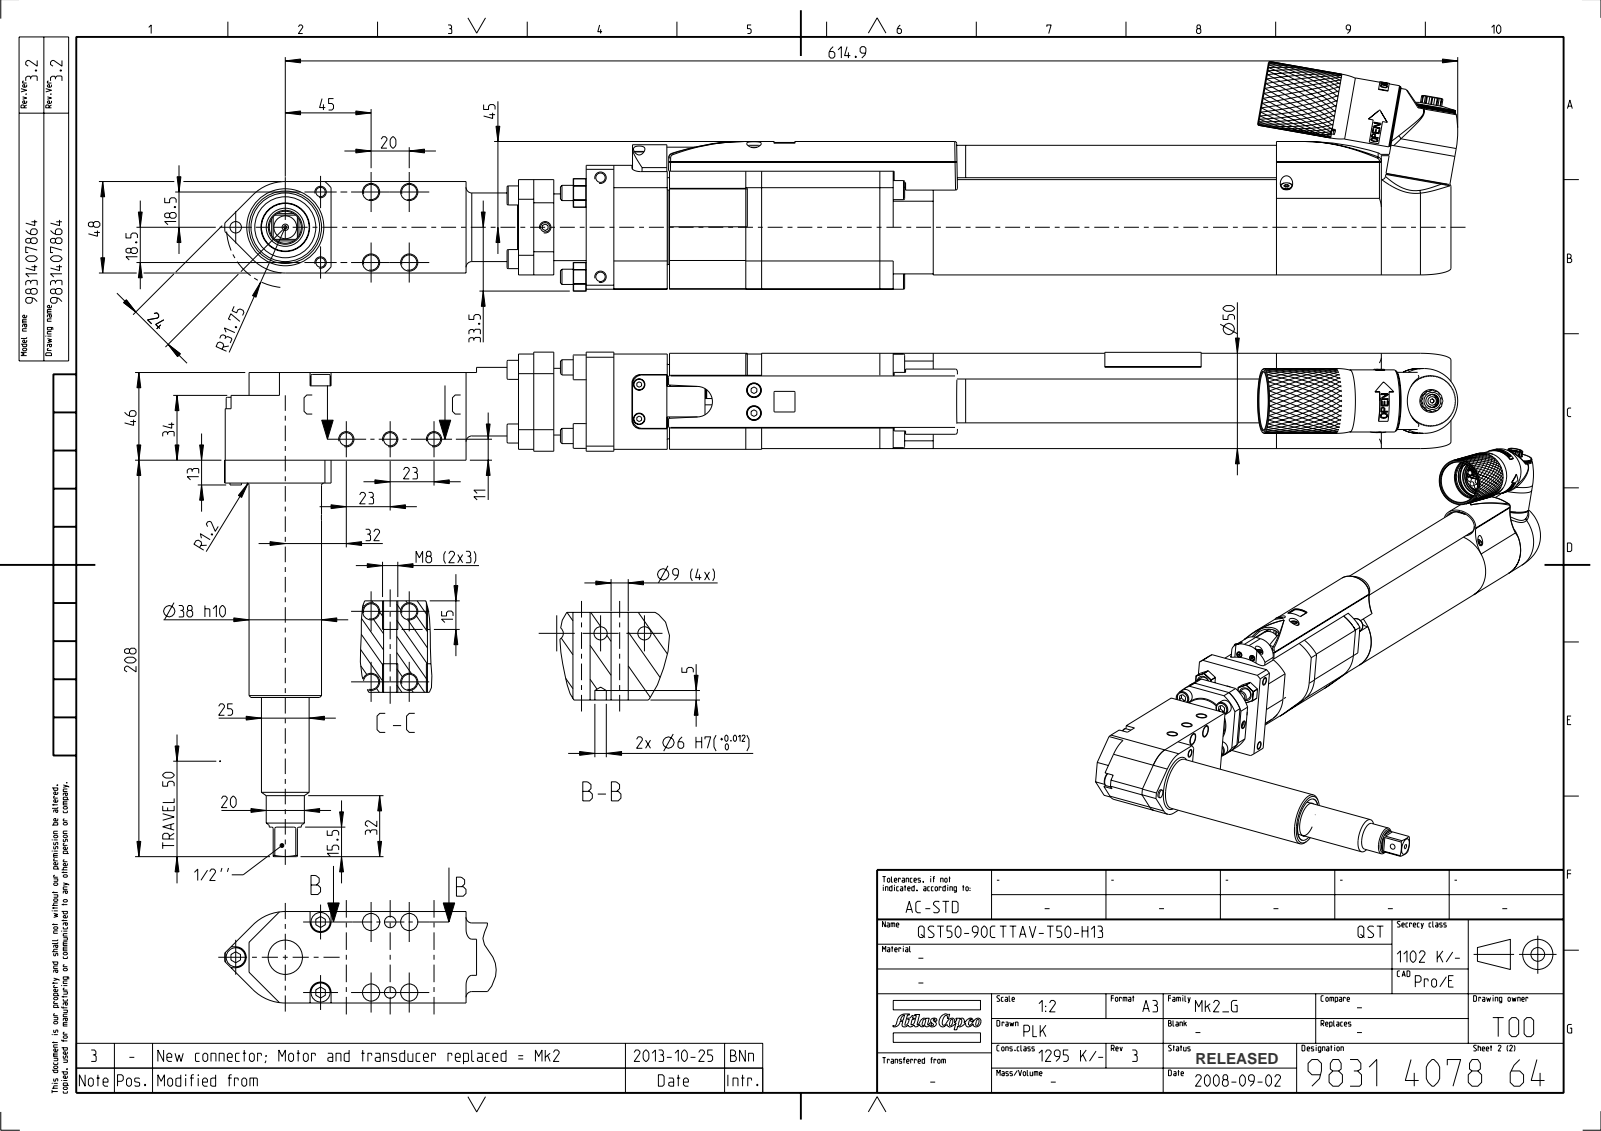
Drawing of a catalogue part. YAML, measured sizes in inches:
part_name: "4230260202; 4230273100; 4220230200; 4220230280_ASM (+8 more)"
step_written_by: "CREO PARAMETRIC BY PTC INC, 2015380 (CONFIG_CONTROL_DESIGN)"
units: inches
bodies: {solids: 298, faces: 10796, planar: 4570, cylindrical: 3230, other: 2996}
overall_size: [28.463, 10.421, 4.743]
volume: 74.36
surface_area: 987.9
round_holes:
  - {diameter: 0.194, count: 14}
  - {diameter: 0.02, count: 12}
  - {diameter: 0.104, count: 11}
  - {diameter: 0.129, count: 11}
  - {diameter: 0.13, count: 11}
  - {diameter: 0.142, count: 11}
  - {diameter: 0.177, count: 10}
  - {diameter: 0.248, count: 10}
  - {diameter: 0.031, count: 9}
  - {diameter: 0.354, count: 9}
  - {diameter: 0.157, count: 8}
  - {diameter: 0.236, count: 8}
round_bosses_or_shafts:
  - {diameter: 0.039, count: 86}
  - {diameter: 0.02, count: 22}
  - {diameter: 0.236, count: 20}
  - {diameter: 0.031, count: 13}
  - {diameter: 0.315, count: 12}
  - {diameter: 0.394, count: 11}
  - {diameter: 0.118, count: 9}
  - {diameter: 0.177, count: 8}
partial_cylinders:
  - {radius: 0.039, count: 109}
  - {radius: 0.008, count: 62}
  - {radius: 0.004, count: 57}
  - {radius: 0.012, count: 46}
  - {radius: 0.02, count: 45}
  - {radius: 0.079, count: 15}
  - {radius: 0.236, count: 14}
  - {radius: 0.011, count: 12}
face_to_face_distances: [0.039, 0.295, 0.335, 1.654, 1.89, 1.811, 1.969, 2.224, 7.835, 1.929]
hole_center_spacings: [0.282, 0.161, 0.292, 0.292, 0.293, 0.719, 0.354, 0.394]
